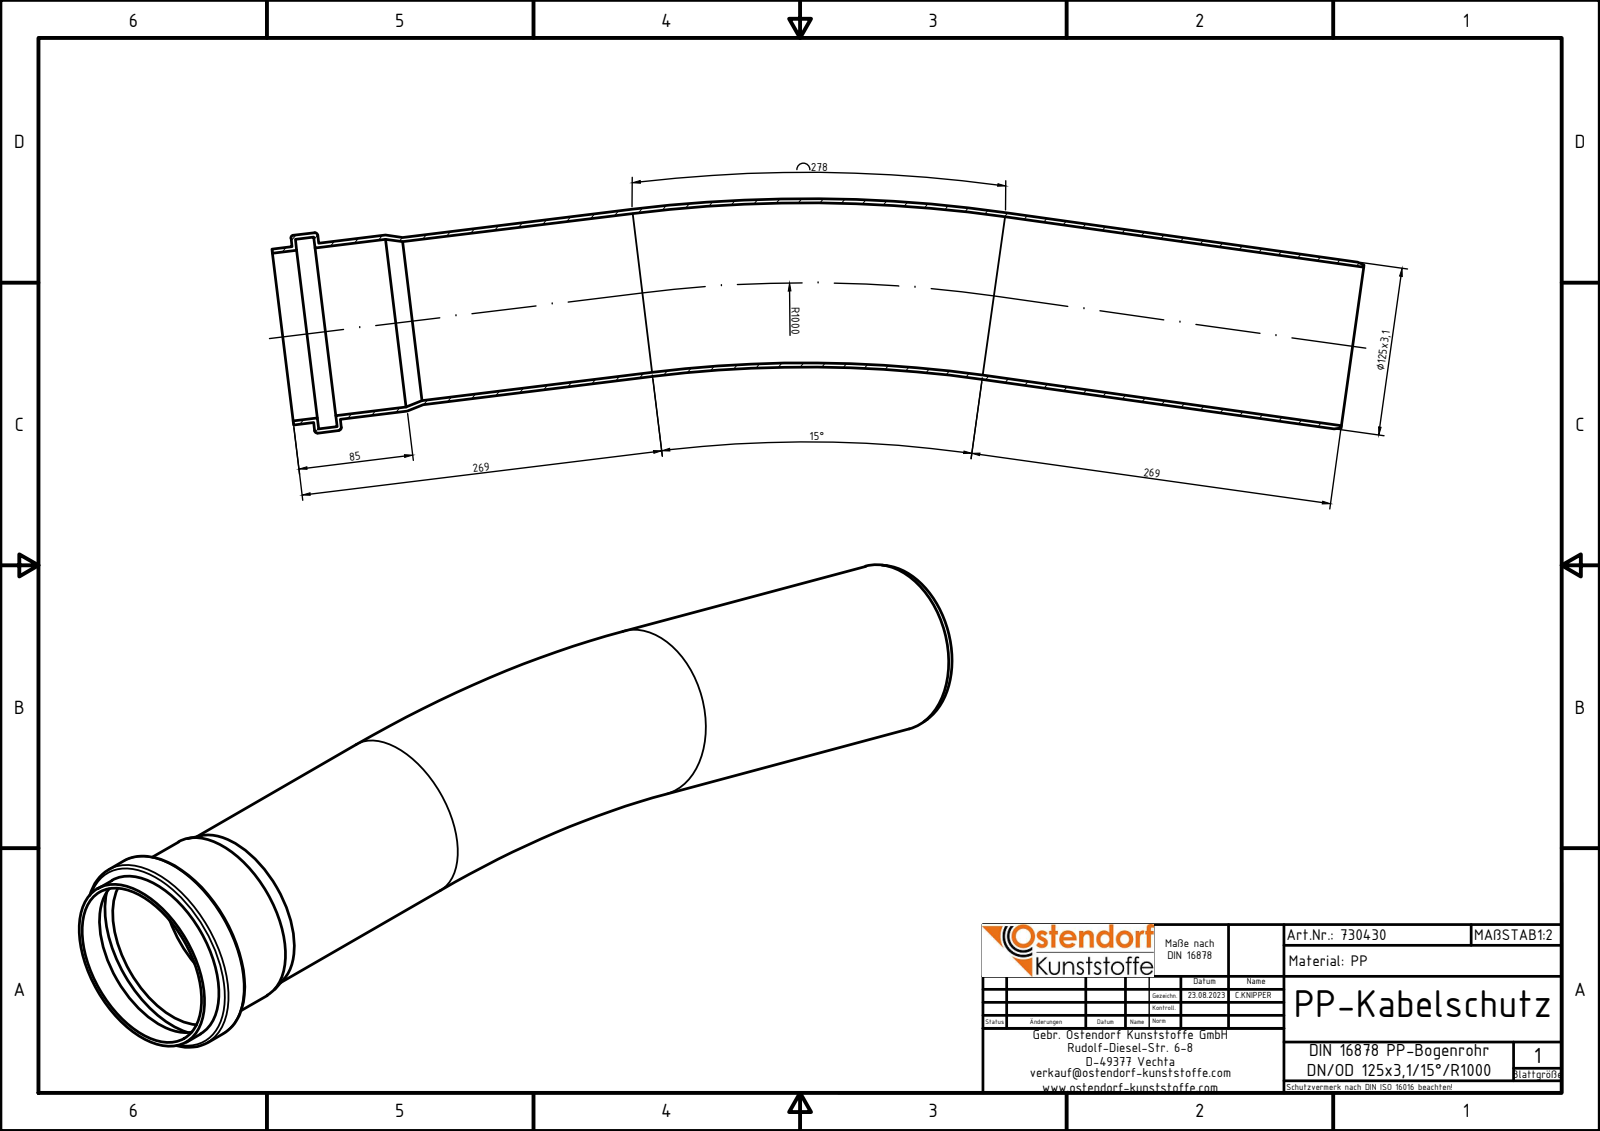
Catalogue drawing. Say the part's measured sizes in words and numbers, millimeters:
The part is named "PP-Bogenrohr_125x31_R1000_15_SM_35017_730430". Its 3-D file was written by "Autodesk Inventor 2024 (AUTOMOTIVE_DESIGN)". It is 1 solid with 23 faces: 6 planar, 10 cylindrical and 7 other. Overall it measures 803.48 by 236.77 by 148 millimeters. Its volume is 978 312 cubic millimeters and its surface area 633 688 square millimeters. Round holes: 2 of diameter 118.8, 1 of diameter 125.4, 1 of diameter 141.8. Round bosses or shafts: 2 of diameter 125, 1 of diameter 148, 1 of diameter 131.6. The main face-to-face distances are 3.1, 16.9, 13.8, 20, 15, 18.1, 31.9, 35.
